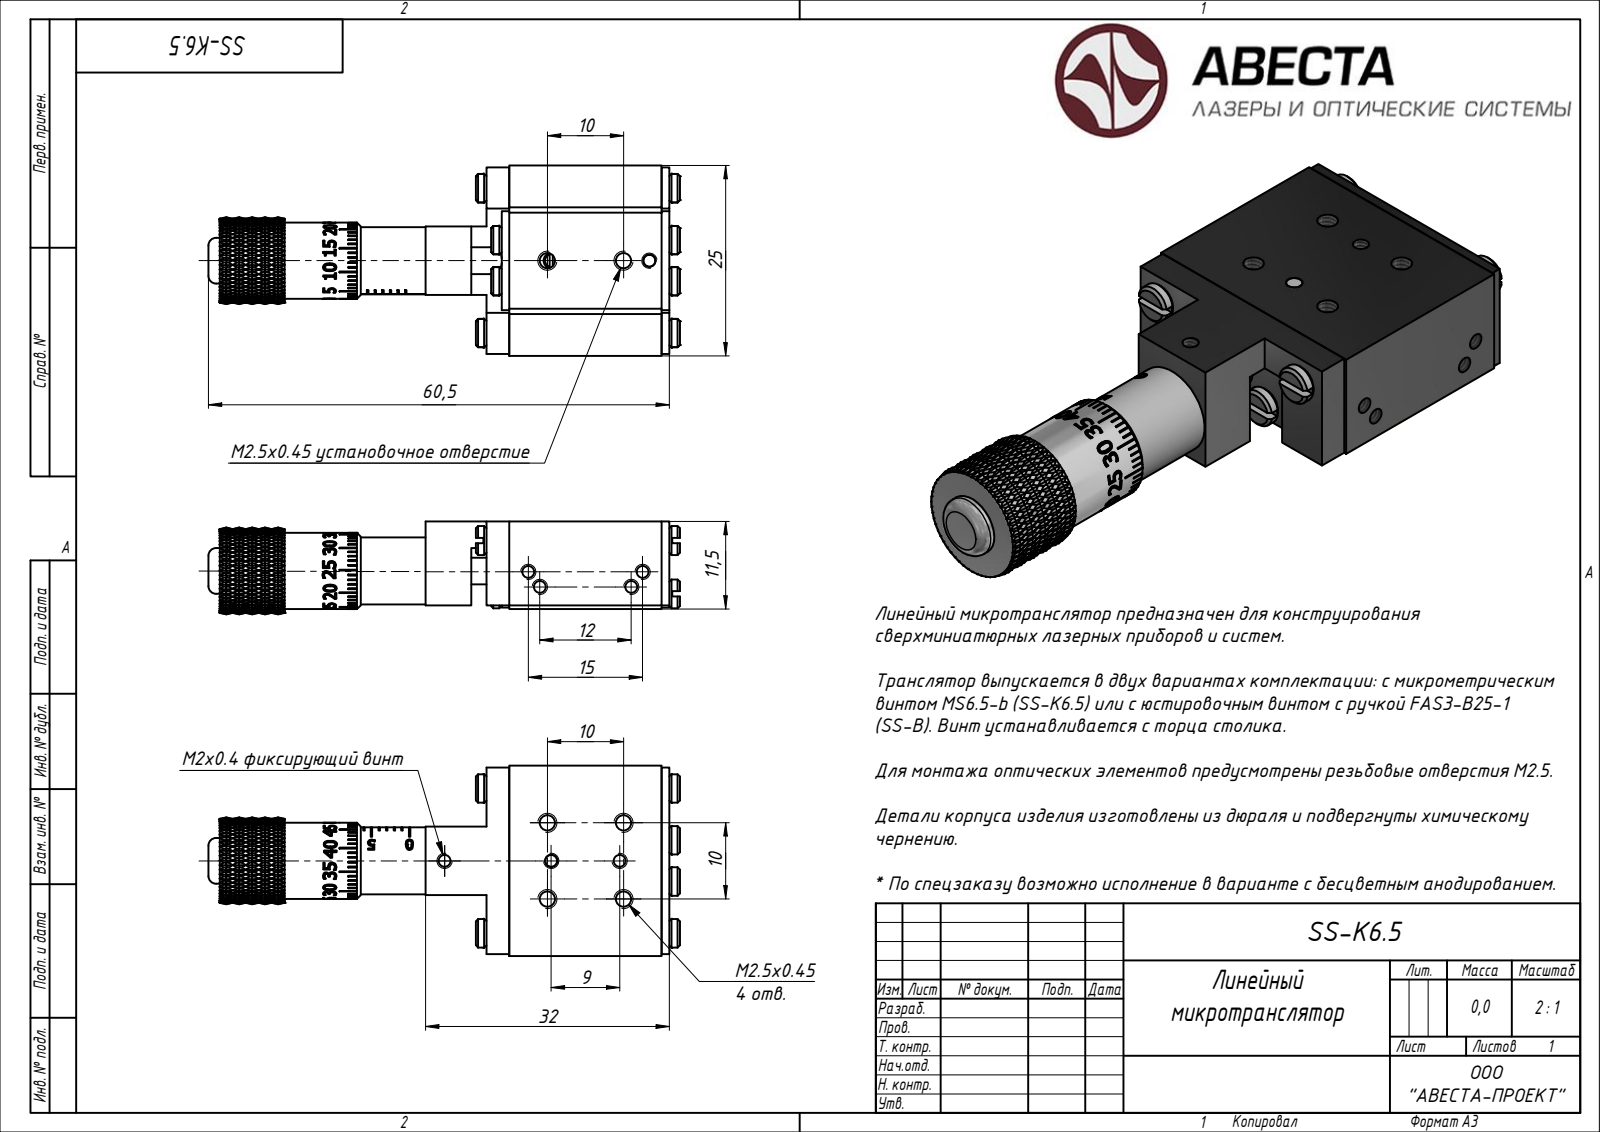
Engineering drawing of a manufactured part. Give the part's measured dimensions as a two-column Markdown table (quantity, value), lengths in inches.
| quantity | value |
| --- | --- |
| STEP written by | Rhino 7.34 (AUTOMOTIVE_DESIGN) |
| units | inches |
| bodies | 2 solids, 2315 faces (1810 planar, 231 cylindrical, 274 other) |
| overall size | 2.437 × 0.984 × 0.48 |
| volume | 0.5 in³ |
| surface area | 10.84 in² |
| round holes (diameter × count) | 0.079 × 6, 0.062 × 5, 0.062 × 1, 0.157 × 1 |
| round bosses / shafts (diameter × count) | 0.079 × 6, 0.15 × 4, 0.059 × 2, 0.433 × 1, 0.394 × 1, 0.346 × 1, 0.236 × 1, 0.138 × 1 |
| partial cylindrical surfaces (radius × count) | 0.059 × 4, 0.031 × 3, 0.031 × 3, 0.173 × 1, 0.193 × 1 |
| main face-to-face distances | 0.433, 0.043, 0.224, 0.453, 0.02, 0.244, 0.283, 0.984, 0.15, 0.303 |
| hole center spacings | 0.394, 0.197, 0.44, 0.198, 0.423, 0.557, 0.567, 0.946 |
